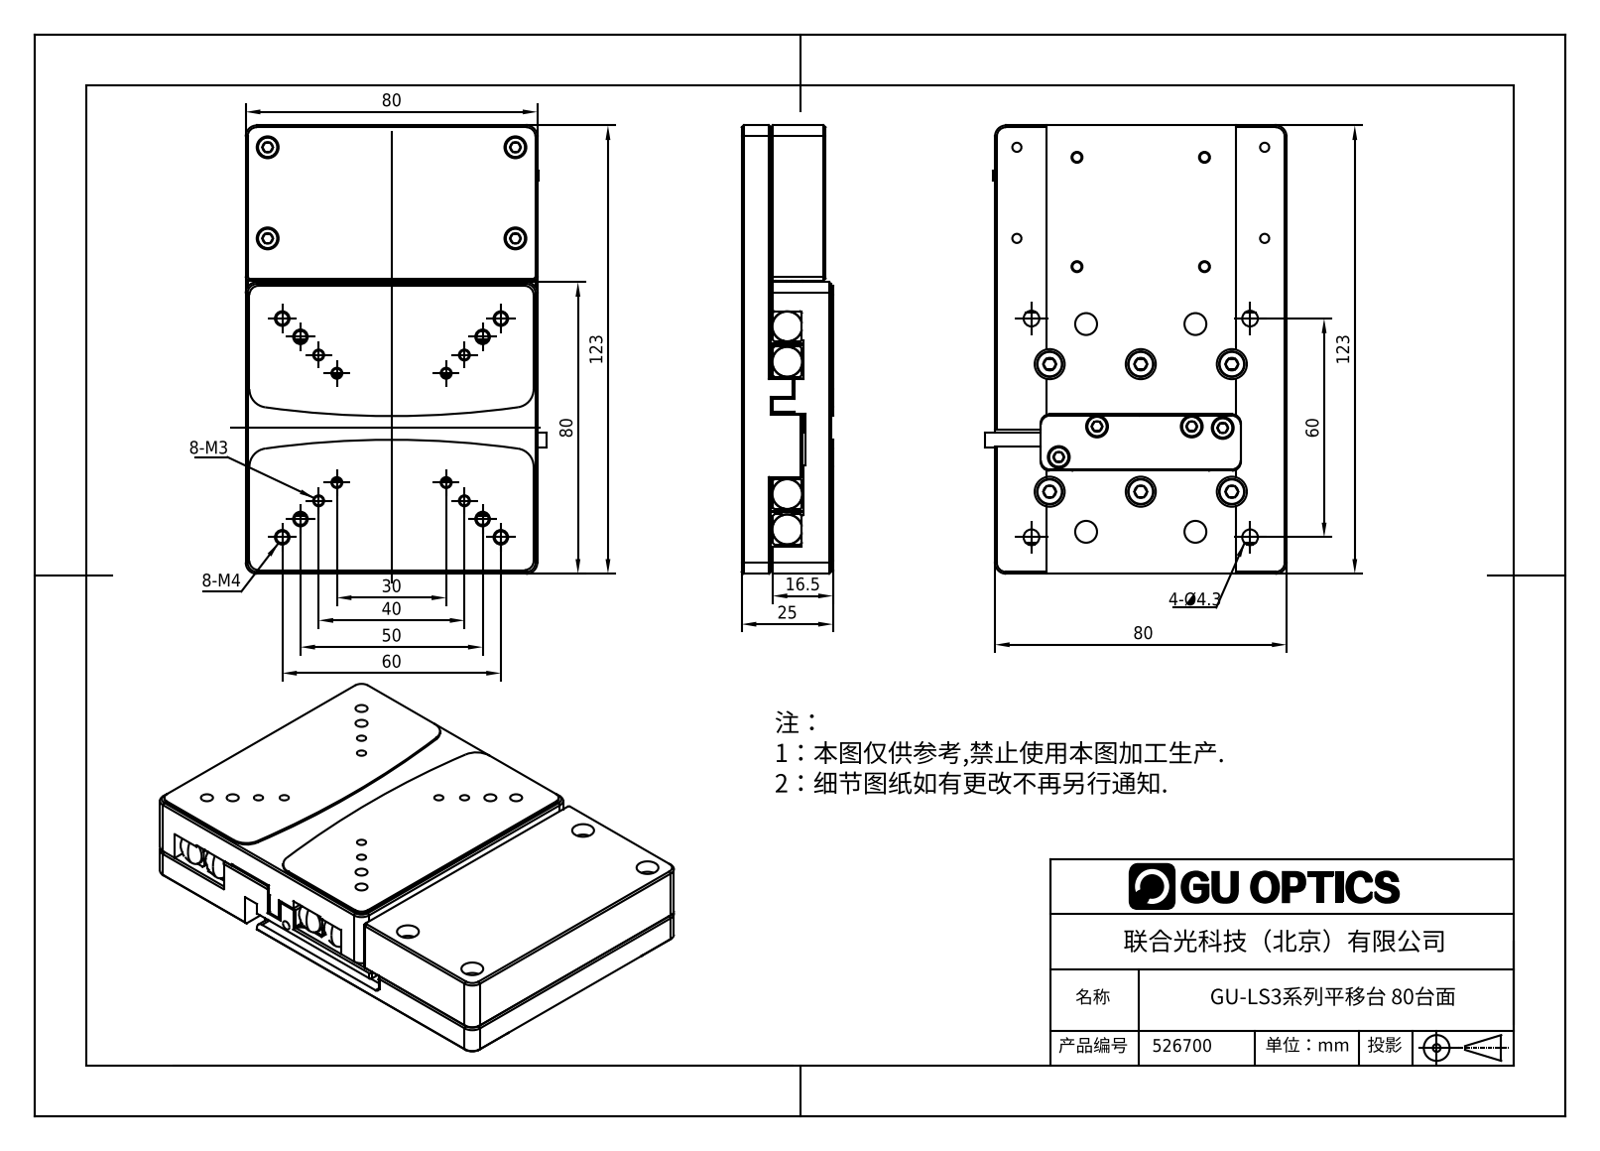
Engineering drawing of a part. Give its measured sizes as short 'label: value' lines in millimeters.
name: GU-LS3系列平移台 80台面
written by: SolidWorks 2016 (CONFIG_CONTROL_DESIGN)
unit: mm
bodies: 0 solids, 1853 faces (875 planar, 495 cylindrical, 483 other)
size: 123 × 80 × 25
holes: 25× ⌀2.5, 23× ⌀3.3, 20× ⌀6, 10× ⌀4.3, 8× ⌀3, 6× ⌀8.25, 4× ⌀3.2, 4× ⌀8, 2× ⌀6.5
bosses: 41× ⌀3, 17× ⌀4, 10× ⌀2.46, 8× ⌀5.5, 6× ⌀7, 6× ⌀3.24, 4× ⌀6, 4× ⌀3.2
rounds: 14× R2.5, 12× R3, 9× R2, 6× R1, 6× R3.2, 4× R5, 2× R0.5, 2× R3.25
face distances: 8, 0.5, 8.5, 16.5, 17, 7.5, 3, 2, 24.5, 6
hole spacings: 7.07, 25, 50, 14.14, 27.31, 35.36, 41.23, 42.5
